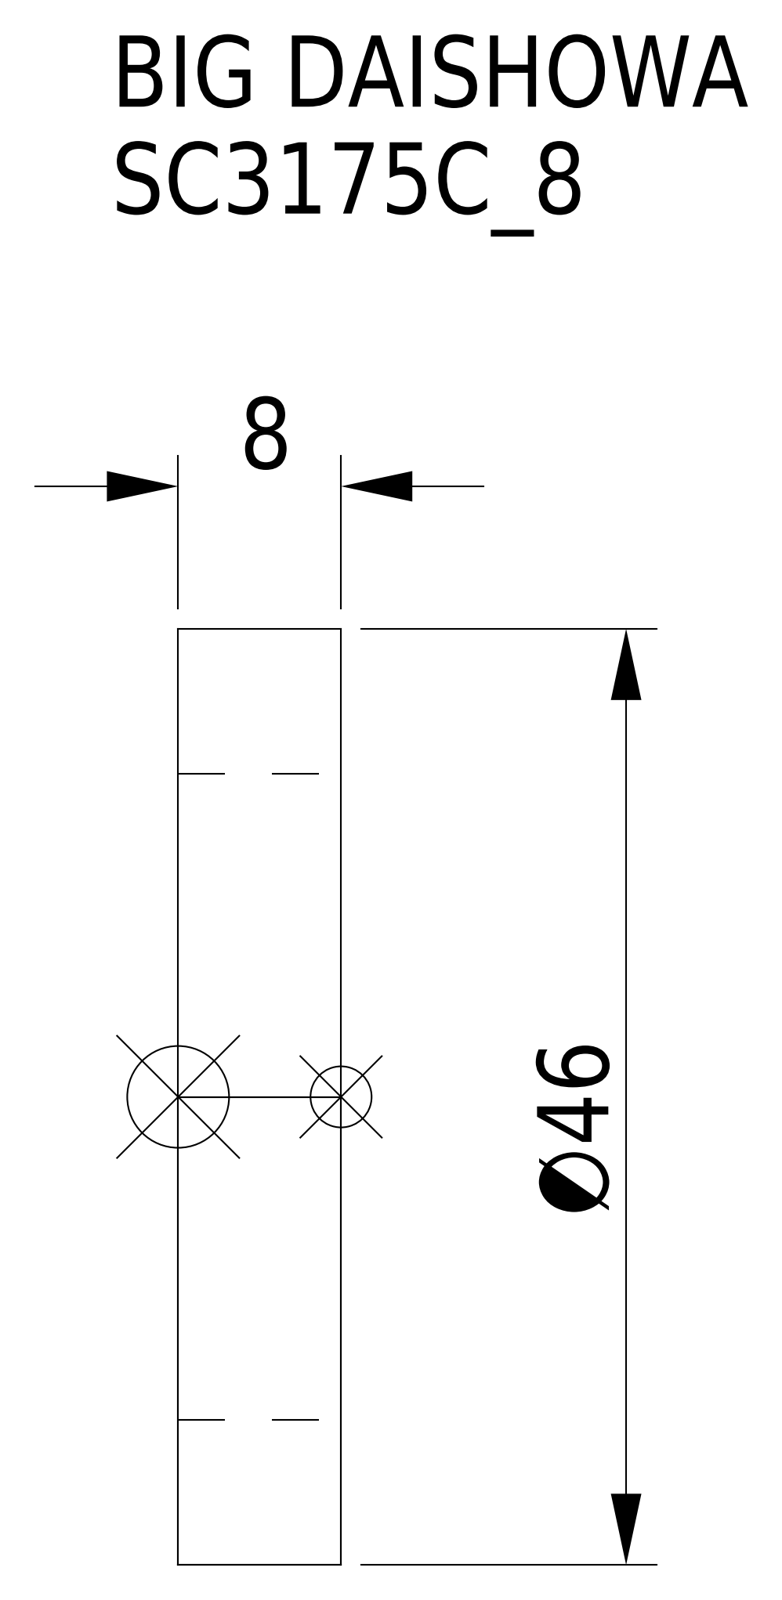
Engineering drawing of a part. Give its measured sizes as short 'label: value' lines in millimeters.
name: SC3175C_8
written by: CREO PARAMETRIC BY PTC INC, 2016380 (AUTOMOTIVE_DESIGN)
unit: mm
bodies: 1 solid, 8 faces (5 planar, 3 cylindrical, 0 other)
size: 46 × 46 × 8
volume: 6 727 mm³; area: 3 699 mm²
holes: 1× ⌀31.75
bosses: 1× ⌀46
face distances: 8, 8.1
